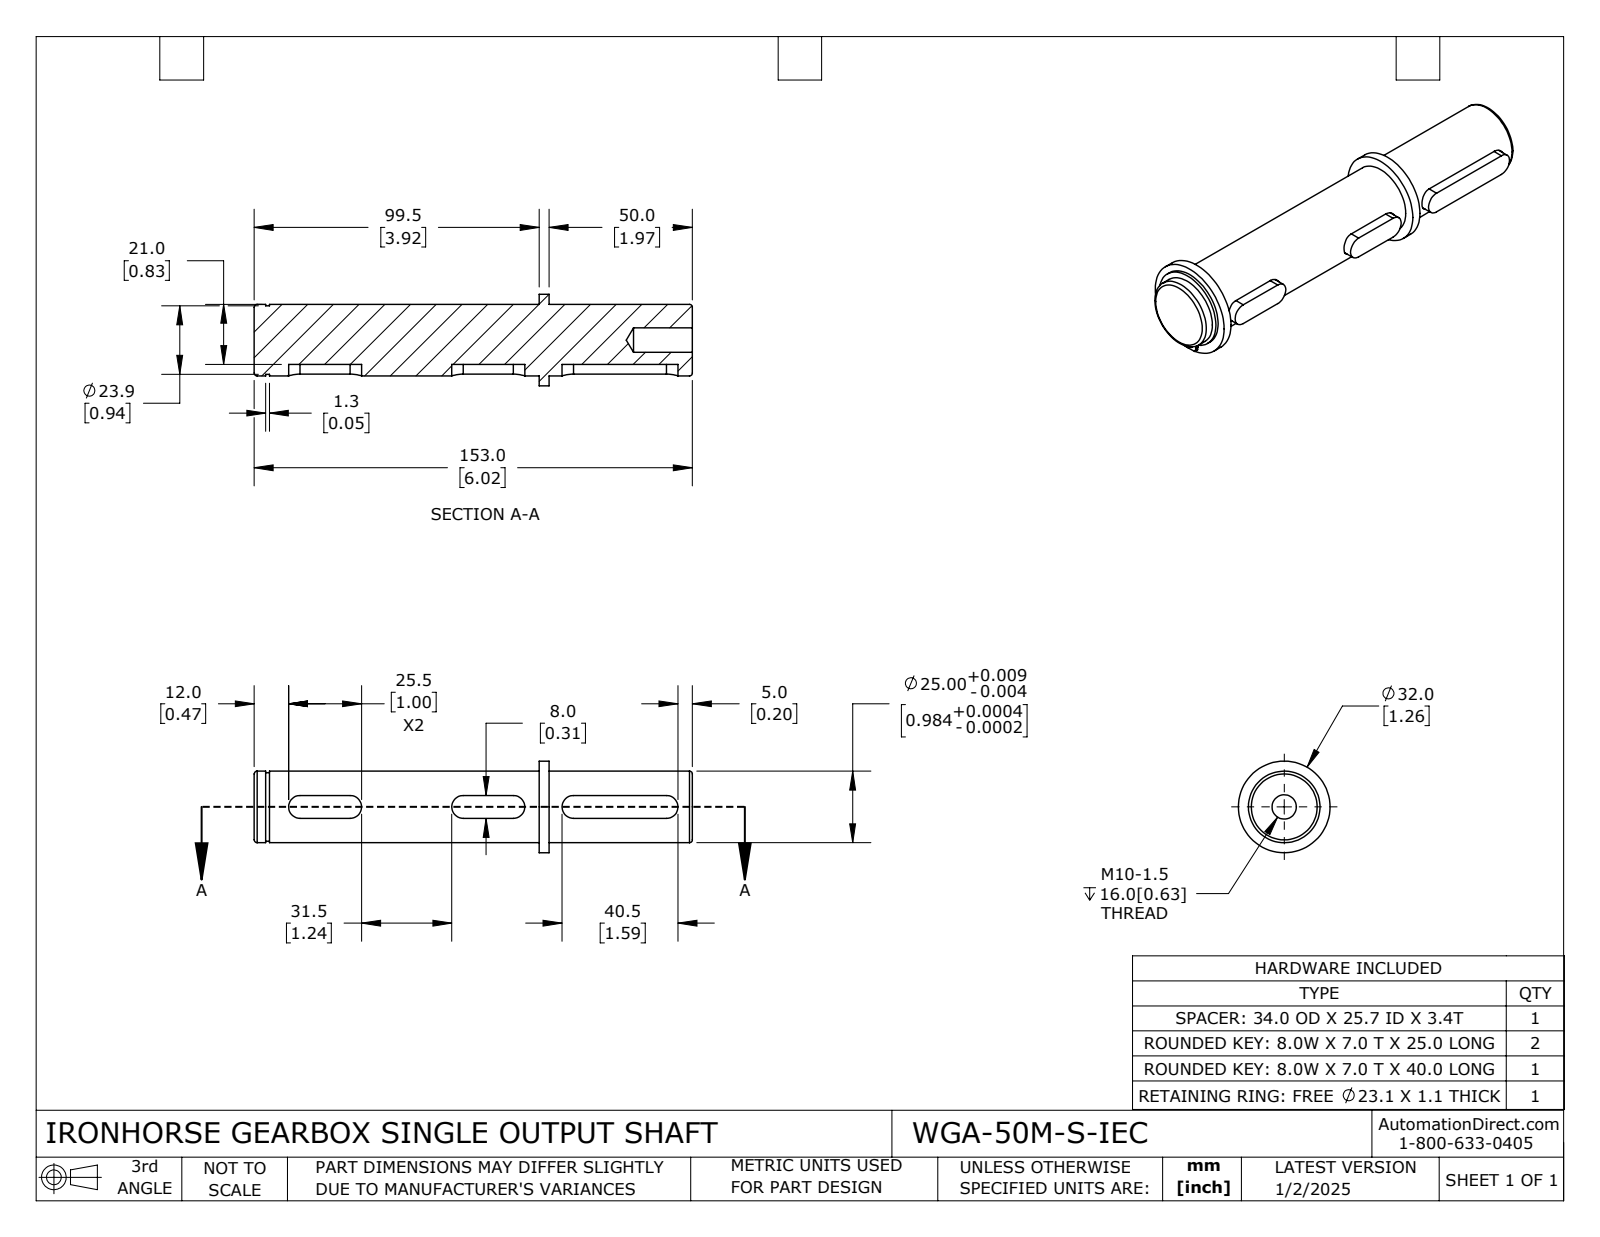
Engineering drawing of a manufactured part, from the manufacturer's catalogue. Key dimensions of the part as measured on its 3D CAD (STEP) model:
Part name (STEP PRODUCT): WGA-50M-S-IEC
STEP written by: SolidWorks 2024 (CONFIG_CONTROL_DESIGN)
Units: millimetres
Bodies: 6 solids, 91 faces (37 planar, 48 cylindrical, 6 other)
Overall size (bounding box): 153 × 34 × 34
Volume: 78 573 mm³ · Surface area: 19 815 mm²
Round holes (diameter × count): ⌀1.9 ×2, ⌀8.5 ×1, ⌀23.5 ×1, ⌀25.7 ×1
Round bosses / shafts (diameter × count): ⌀34 ×1, ⌀32 ×1, ⌀28.05 ×1, ⌀25 ×1, ⌀23.9 ×1
Partial cylindrical surfaces — rounded edges, fillets, slot ends (radius × count): R4 ×12, R0.5 ×2, R2.5 ×2
Main face-to-face distances: 8, 7, 5.3, 8.7, 3.4, 153, 147.7, 144.3, 99.5, 103
Hole centre spacings: 14.23, 3
